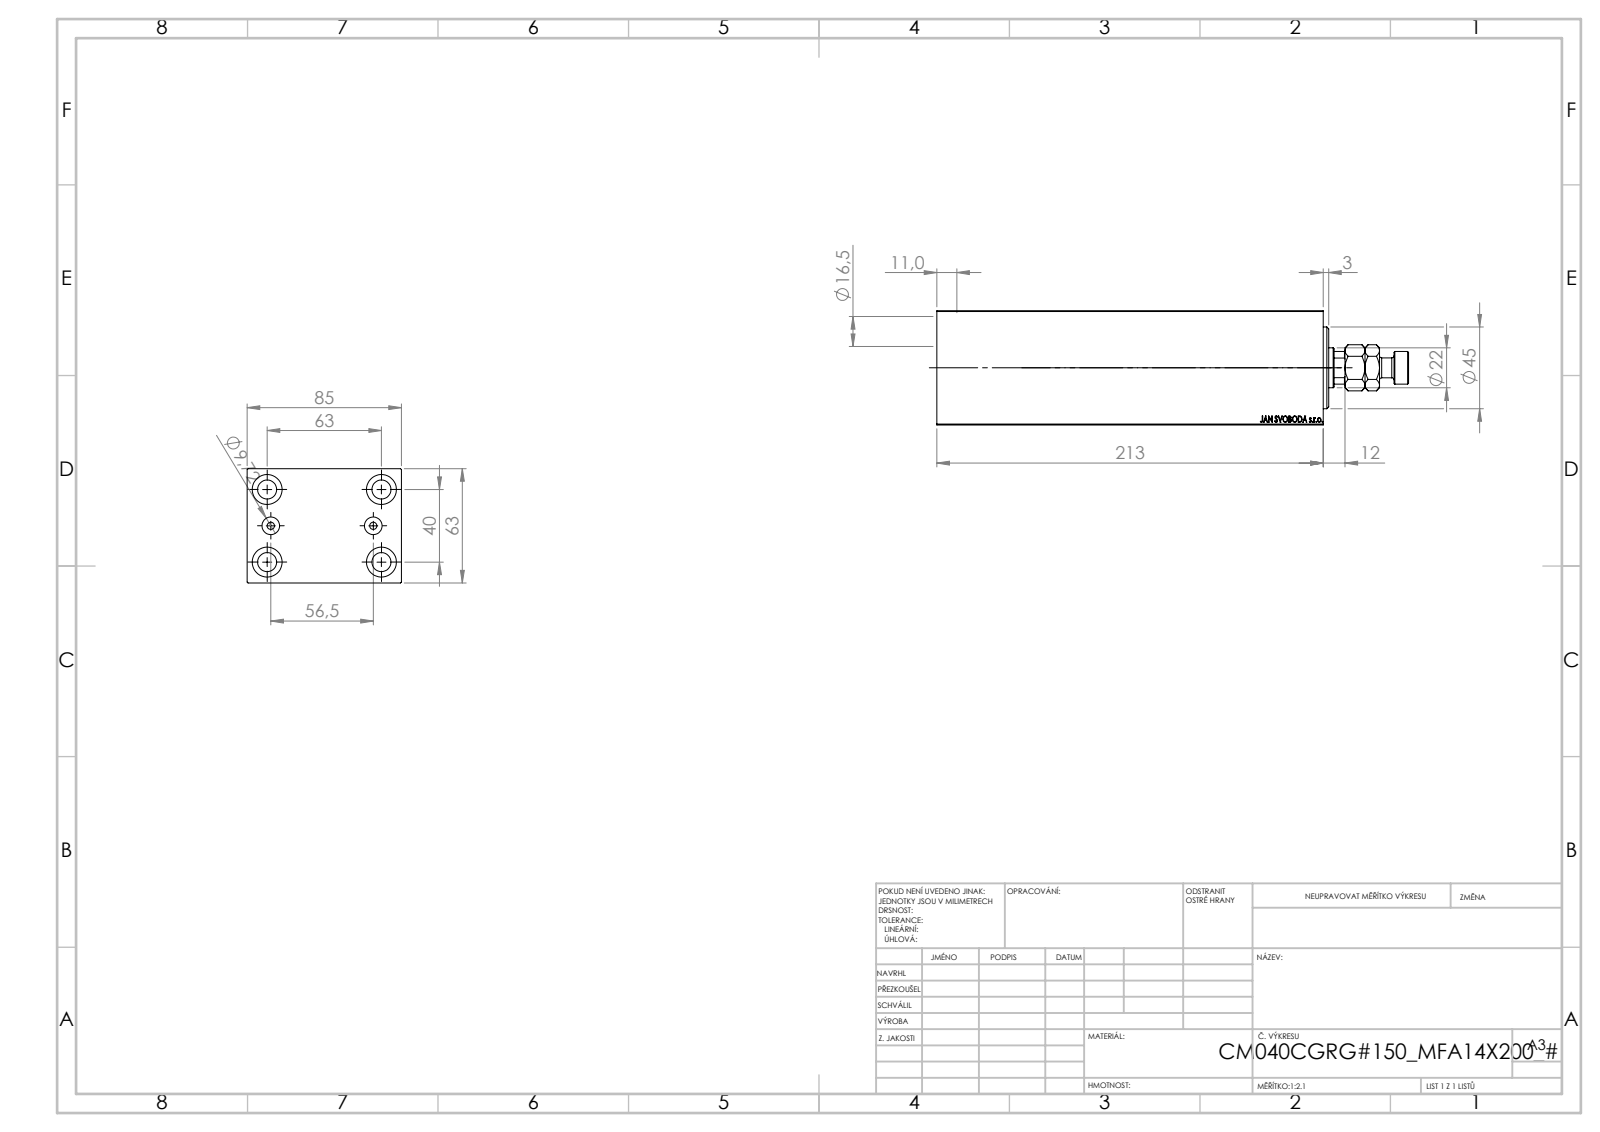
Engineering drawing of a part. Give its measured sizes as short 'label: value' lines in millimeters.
name: V450CM_VC_B; V450CM_C_Body; MFA; V450CM_C_VCP
written by: SolidWorks 2019 (CONFIG_CONTROL_DESIGN)
unit: mm
bodies: 4 solids, 910 faces (424 planar, 60 cylindrical, 426 other)
size: 260 × 85 × 63
volume: 933 160 mm³; area: 162 434 mm²
holes: 4× ⌀10.5, 4× ⌀16.5, 2× ⌀4, 2× ⌀9.72, 1× ⌀12.5, 1× ⌀22, 1× ⌀25.5, 1× ⌀40, 1× ⌀42, 1× ⌀45
bosses: 1× ⌀18, 1× ⌀11
rounds: 1× R10.5
face distances: 63, 85, 12, 201, 213, 1, 189, 11, 202, 190
hole spacings: 37.31, 20.1, 20.5, 40, 61.82, 63, 64.2, 74.63
